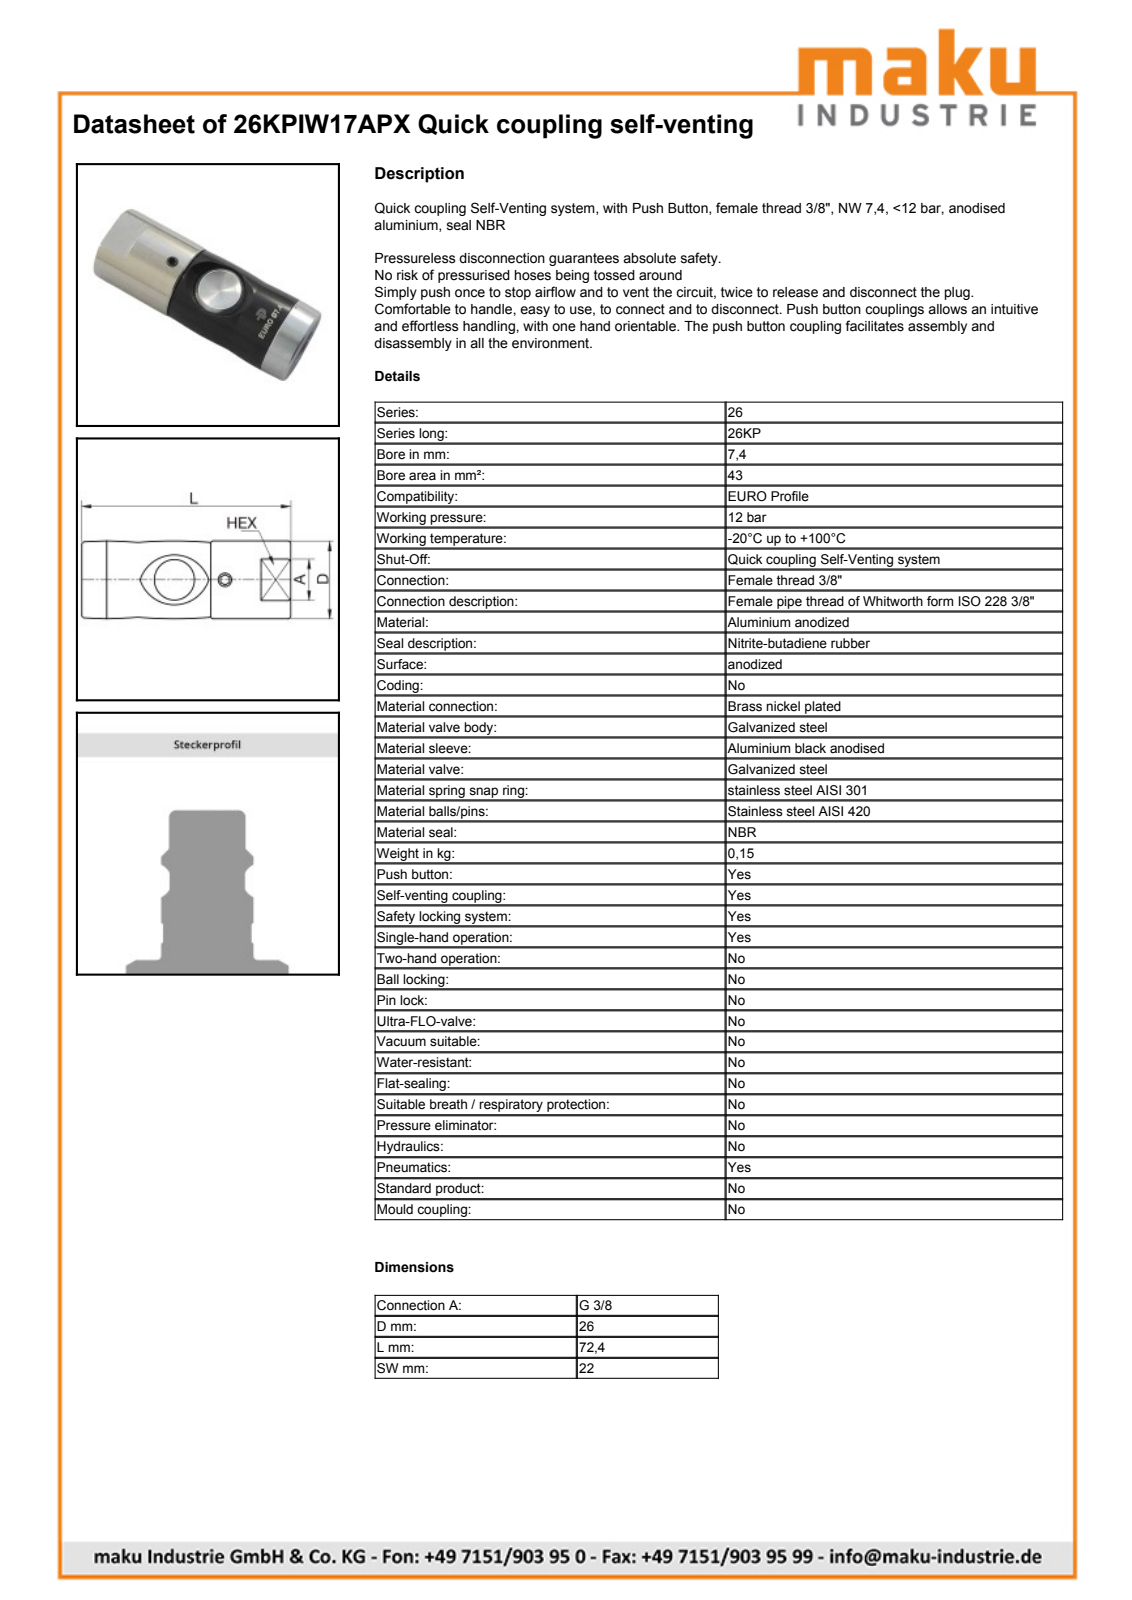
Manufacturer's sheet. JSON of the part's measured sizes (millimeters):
{"part_name": "26KPIW17APX", "step_written_by": "Autodesk Inventor 2019 (AUTOMOTIVE_DESIGN)", "units": "millimeters", "bodies": {"solids": 39, "faces": 259, "planar": 72, "cylindrical": 82, "other": 105}, "overall_size": [72.4, 26, 26], "volume_mm3": 39207, "surface_area_mm2": 25047, "round_holes": [[12.4, 2], [3.5, 1], [6.5, 1], [7, 1], [9.65, 1], [10.1, 1], [10.6, 1], [11, 1], [12.1, 1], [12.25, 1], [12.8, 1], [13.6, 1]], "round_bosses_or_shafts": [[26, 1], [22, 1], [18.1, 1], [17.8, 1], [16.5, 1], [16.23, 1], [15.8, 1], [14.6, 1]], "partial_cylinders_radius": [[6.2, 2], [4.4, 1]], "face_to_face_distances": [43.4, 8.4, 35, 29, 64, 72.4, 13.92, 15.08, 50.08, 58.48], "hole_center_spacings": [0.6, 0.7, 1.3, 17.05]}
